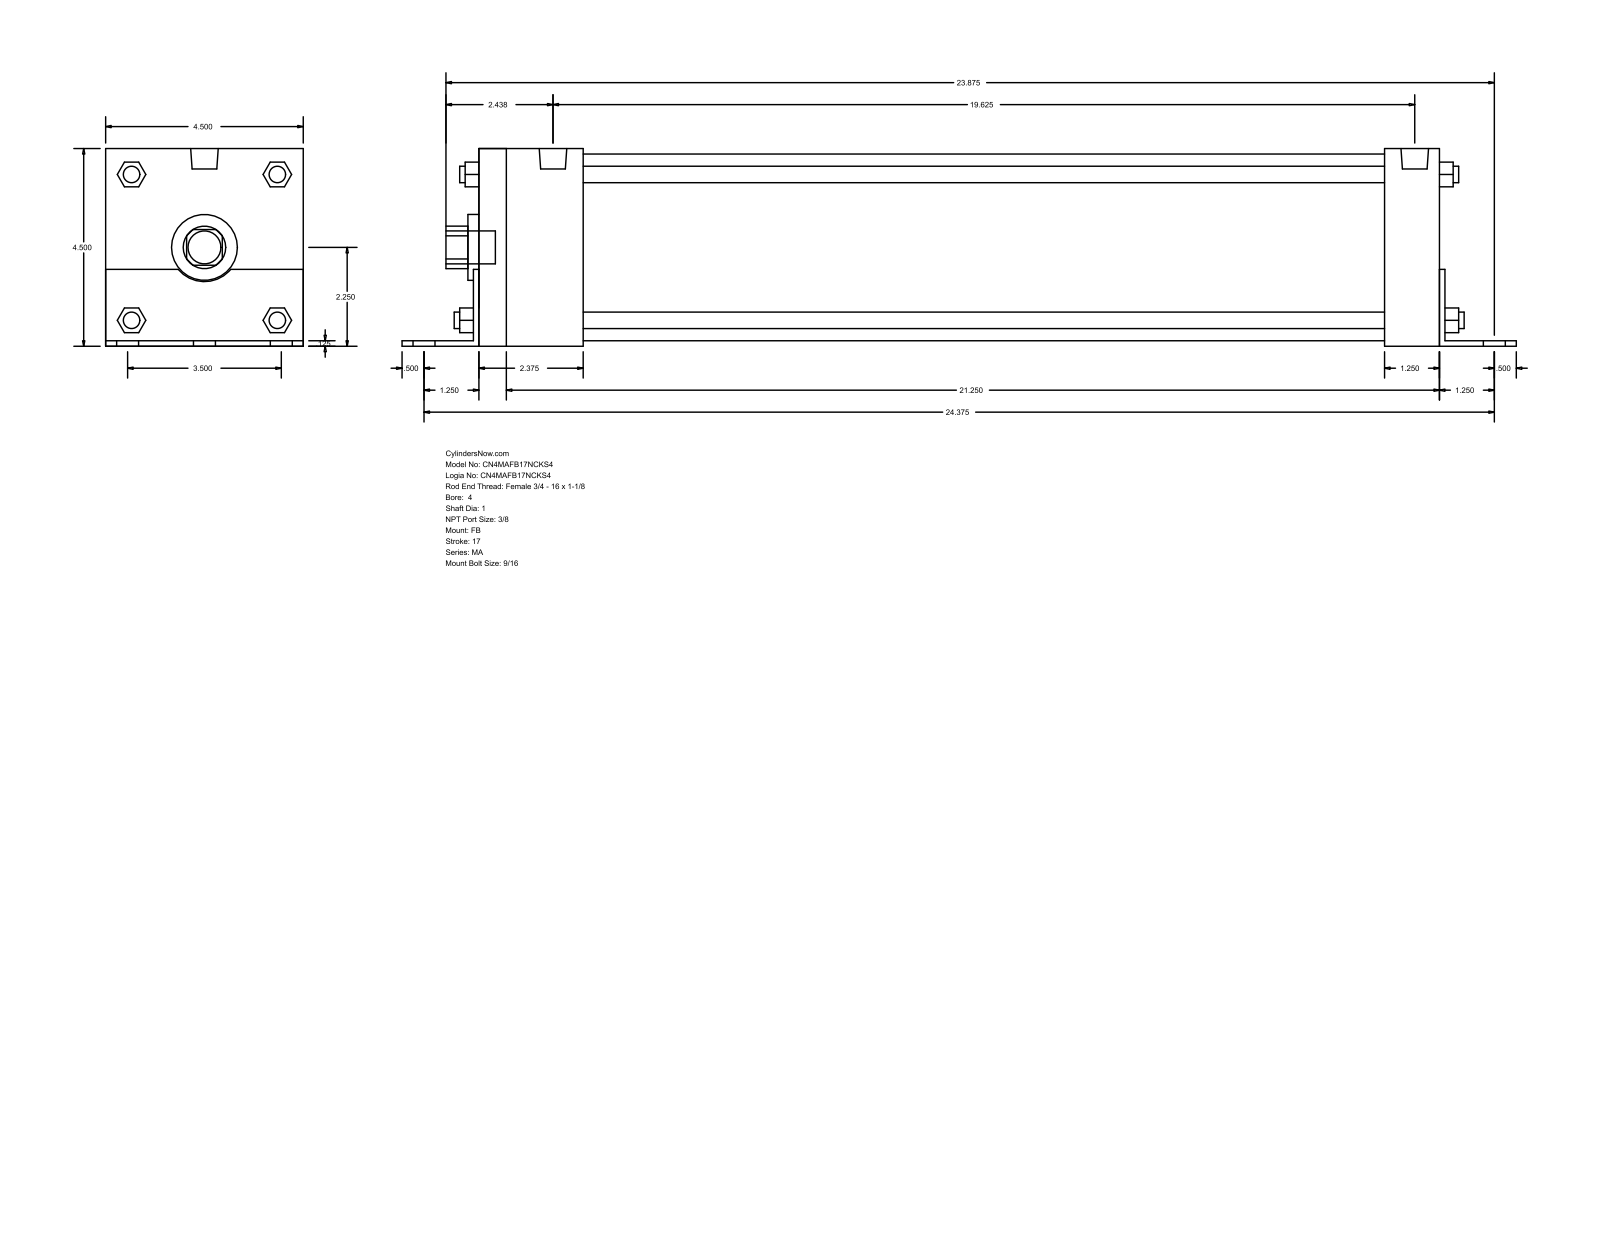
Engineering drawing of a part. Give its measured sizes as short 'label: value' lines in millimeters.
name: MA_FB__0400_1
written by: GSSL Pune (CONFIG_CONTROL_DESIGN)
unit: mm
bodies: 0 solids, 140 faces (105 planar, 35 cylindrical, 0 other)
size: 644.52 × 114.35 × 114.3
holes: 1× ⌀25.4, 1× ⌀38.1, 1× ⌀107.95
bosses: 6× ⌀14.29, 4× ⌀11.11, 4× ⌀9.53, 2× ⌀15.93, 1× ⌀19.05
rounds: 1× R12.29, 1× R19.81
face distances: 114.3, 3.17, 114.35, 3.12, 111.18, 555.62, 3.18, 561.97, 558.8, 558.79
